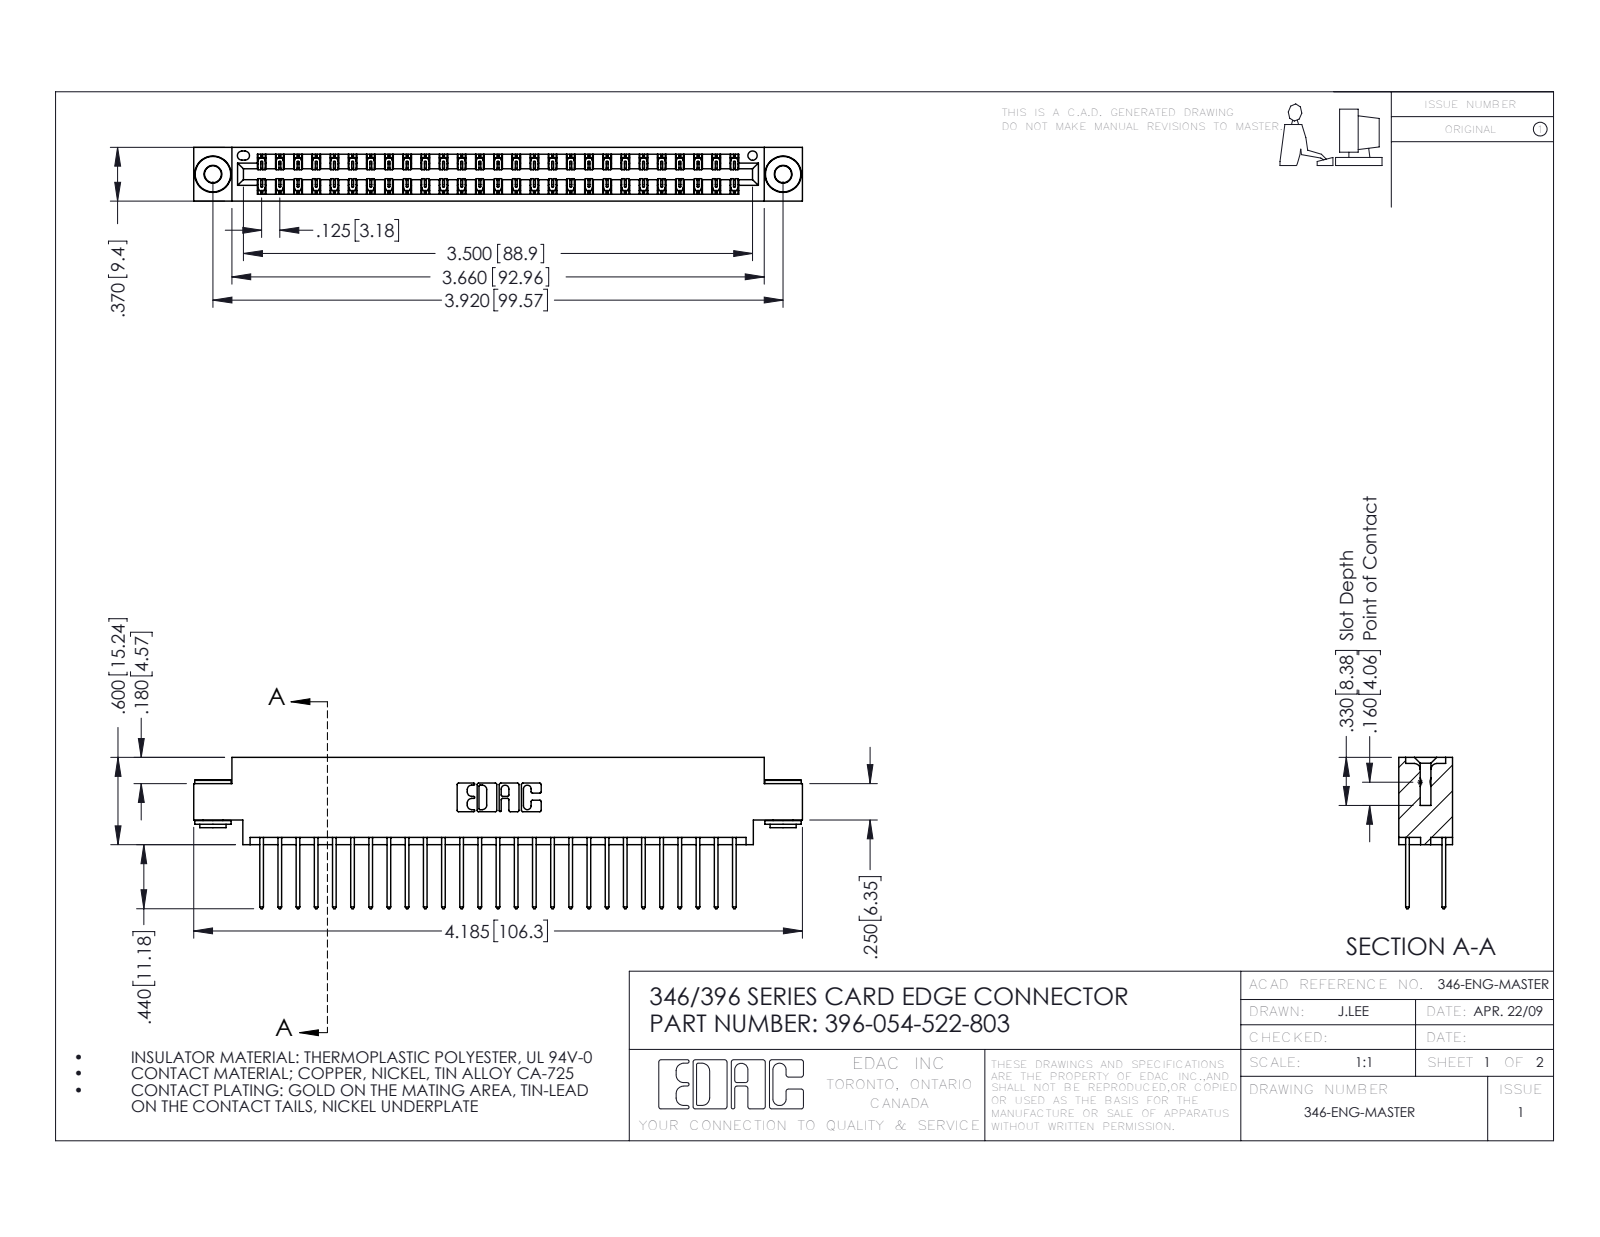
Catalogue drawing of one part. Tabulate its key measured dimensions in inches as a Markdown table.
| quantity | value |
| --- | --- |
| part name | 345-250-002_345-250-002-102; 345-292-001_345-293-122; 346 Part_0.170 Offset - 0.156 Dia-TH; 396-054-522-803 |
| STEP written by | SolidWorks 2016 (CONFIG_CONTROL_DESIGN) |
| units | inches |
| bodies | 57 solids, 2972 faces (1980 planar, 984 cylindrical, 8 other) |
| overall size | 4.185 × 1.04 × 0.37 |
| volume | 0.626 in³ |
| surface area | 23.08 in² |
| round holes (diameter × count) | 0.116 × 2, 0.156 × 2, 0.064 × 1 |
| round bosses / shafts (diameter × count) | 0.25 × 2, 0.18 × 2, 0.136 × 2 |
| partial cylindrical surfaces (radius × count) | 0.006 × 81, 0.01 × 54, 0.01 × 22, 0.007 × 6, 0.031 × 6, 0.026 × 3, 0.014 × 2, 0.022 × 2 |
| main face-to-face distances | 0.048, 0.322, 0.25, 0.37, 0.025, 0.072, 0.298, 0.275, 0.148, 0.222 |
| hole center spacings | 0.246, 3.712, 3.92 |
